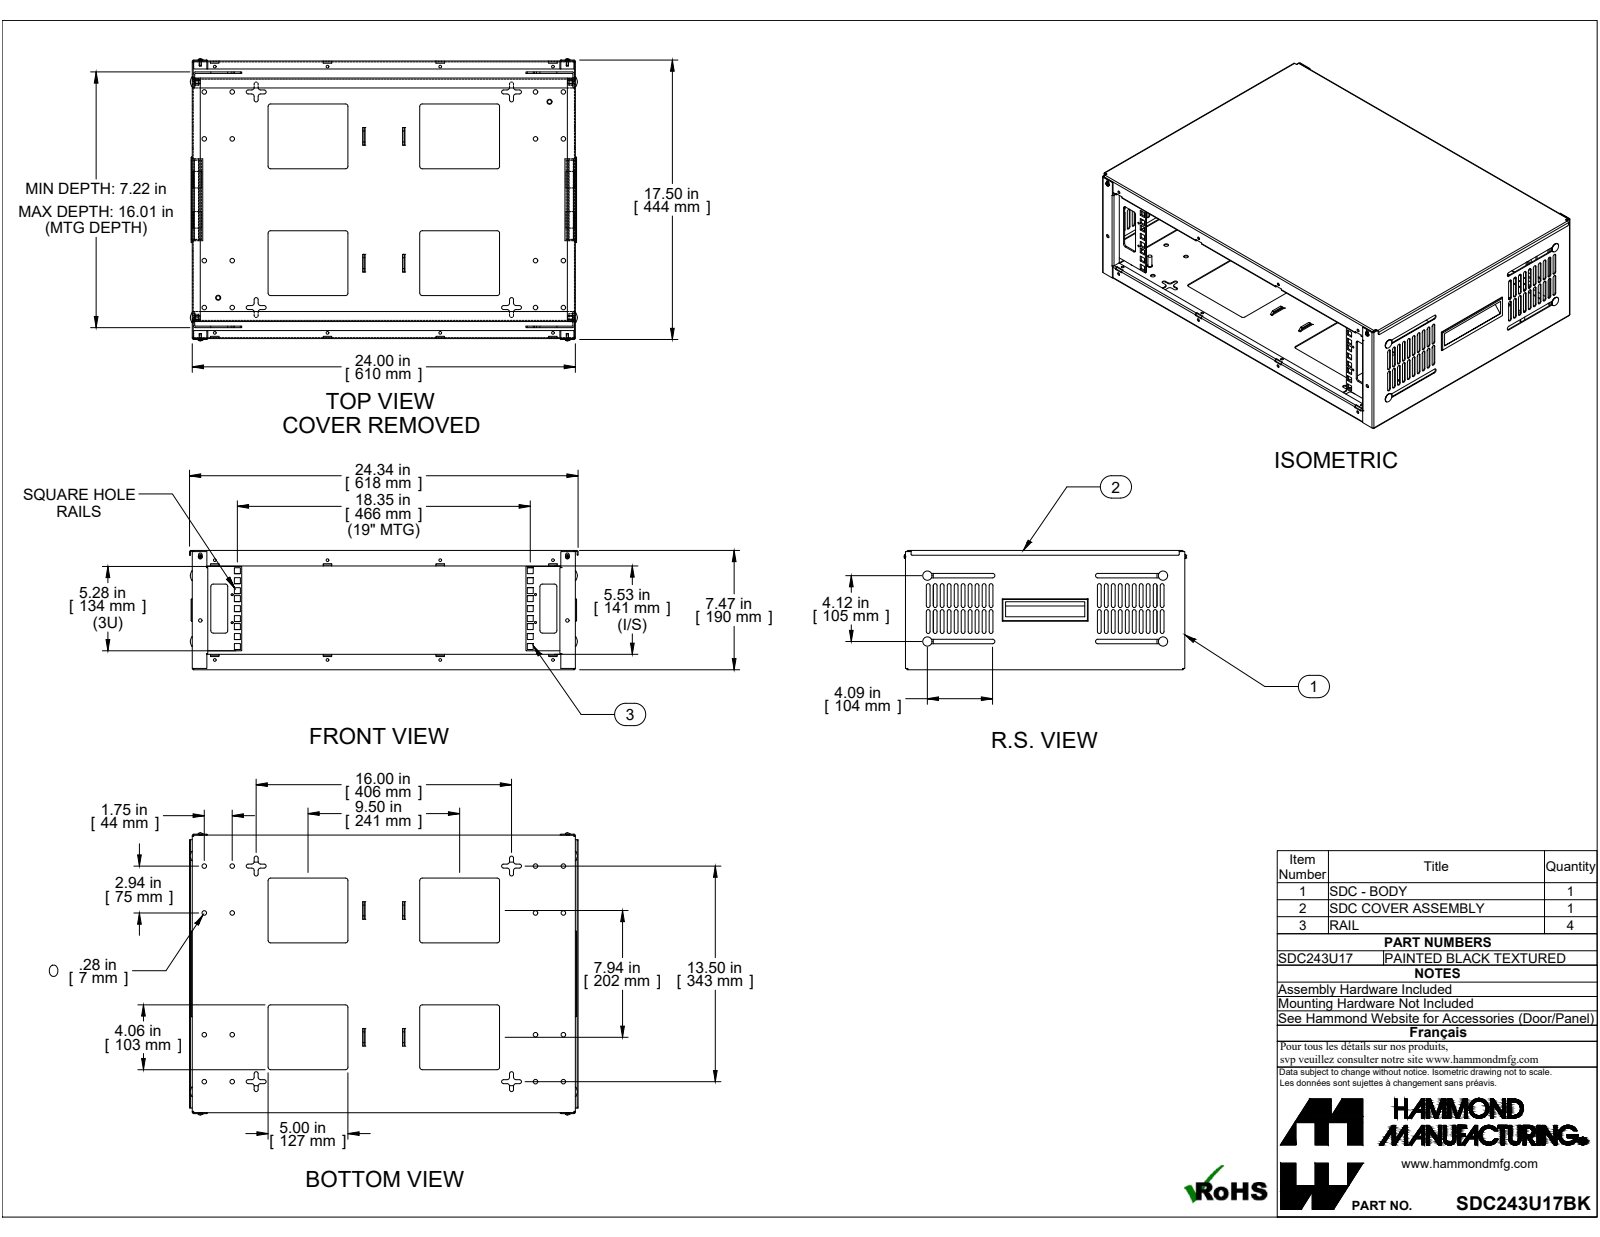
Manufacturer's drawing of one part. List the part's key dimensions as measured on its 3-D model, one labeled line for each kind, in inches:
Part name (STEP PRODUCT): SDC243U17BK
STEP written by: SolidWorks 2019 (CONFIG_CONTROL_DESIGN)
Units: inches
Bodies: 36 solids, 1730 faces (1118 planar, 560 cylindrical, 52 other)
Overall size (bounding box): 24.344 × 17.67 × 7.472
Volume: 78.77 in³ · Surface area: 2 660 in²
Round holes (diameter × count): ⌀0.17 ×16, ⌀0.281 ×16, ⌀0.125 ×8, ⌀0.196 ×4, ⌀0.159 ×2, ⌀0.187 ×2, ⌀0.213 ×2
Round bosses / shafts (diameter × count): ⌀0.25 ×8, ⌀0.58 ×4, ⌀0.313 ×2, ⌀0.28 ×2, ⌀0.187 ×2, ⌀0.138 ×2
Partial cylindrical surfaces — rounded edges, fillets, slot ends (radius × count): R0.118 ×68, R0.157 ×44, R0.029 ×22, R0.086 ×22, R0.025 ×16, R0.125 ×16, R0.117 ×12, R0.03 ×8
Main face-to-face distances: 0.057, 7.415, 7.358, 7.472, 23.943, 23.886, 24, 0.912, 0.072, 6.503
Hole centre spacings: 1.75, 2.937, 3.419, 7.063, 10.563, 10.707, 19.005, 19.085
